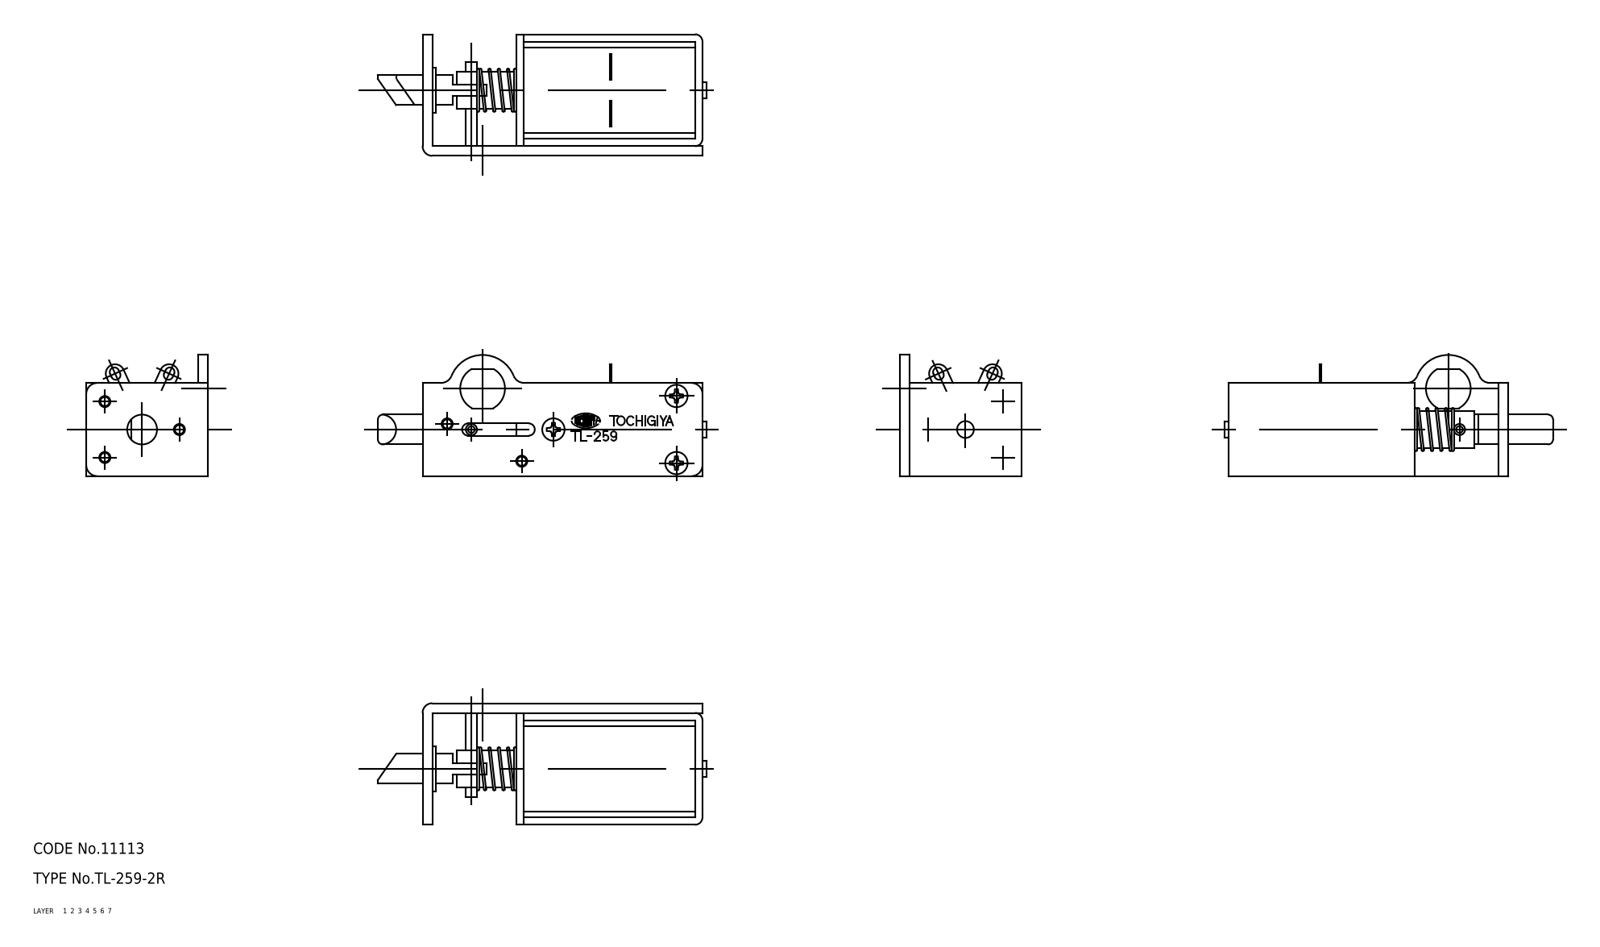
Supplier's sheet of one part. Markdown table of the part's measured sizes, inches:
| quantity | value |
| --- | --- |
| part name | latch; screw; pin; TL_259_2R (+5 more) |
| STEP written by | SolidWorks 2015 (AUTOMOTIVE_DESIGN) |
| units | inches |
| bodies | 10 solids, 256 faces (141 planar, 89 cylindrical, 26 other) |
| overall size | 3.465 × 1.28 × 1.28 |
| volume | 1.865 in³ |
| surface area | 30.69 in² |
| round holes (diameter × count) | 0.118 × 6, 0.126 × 3, 0.071 × 1, 0.472 × 1 |
| round bosses / shafts (diameter × count) | 0.236 × 3, 0.787 × 1, 0.394 × 1, 0.315 × 1, 0.287 × 1, 0.177 × 1 |
| partial cylindrical surfaces (radius × count) | 0.118 × 6, 0.02 × 4, 0.049 × 4, 0.071 × 3, 0.065 × 2, 0.079 × 2, 0.098 × 2, 0.102 × 1 |
| main face-to-face distances | 0.079, 1.098, 0.102, 1.28, 1.177, 1.201, 1.02, 0.181, 0.984, 1.89 |
| hole center spacings | 0.492, 0.841, 1.347, 2.194, 0.263, 0.394, 0.473, 0.591 |
